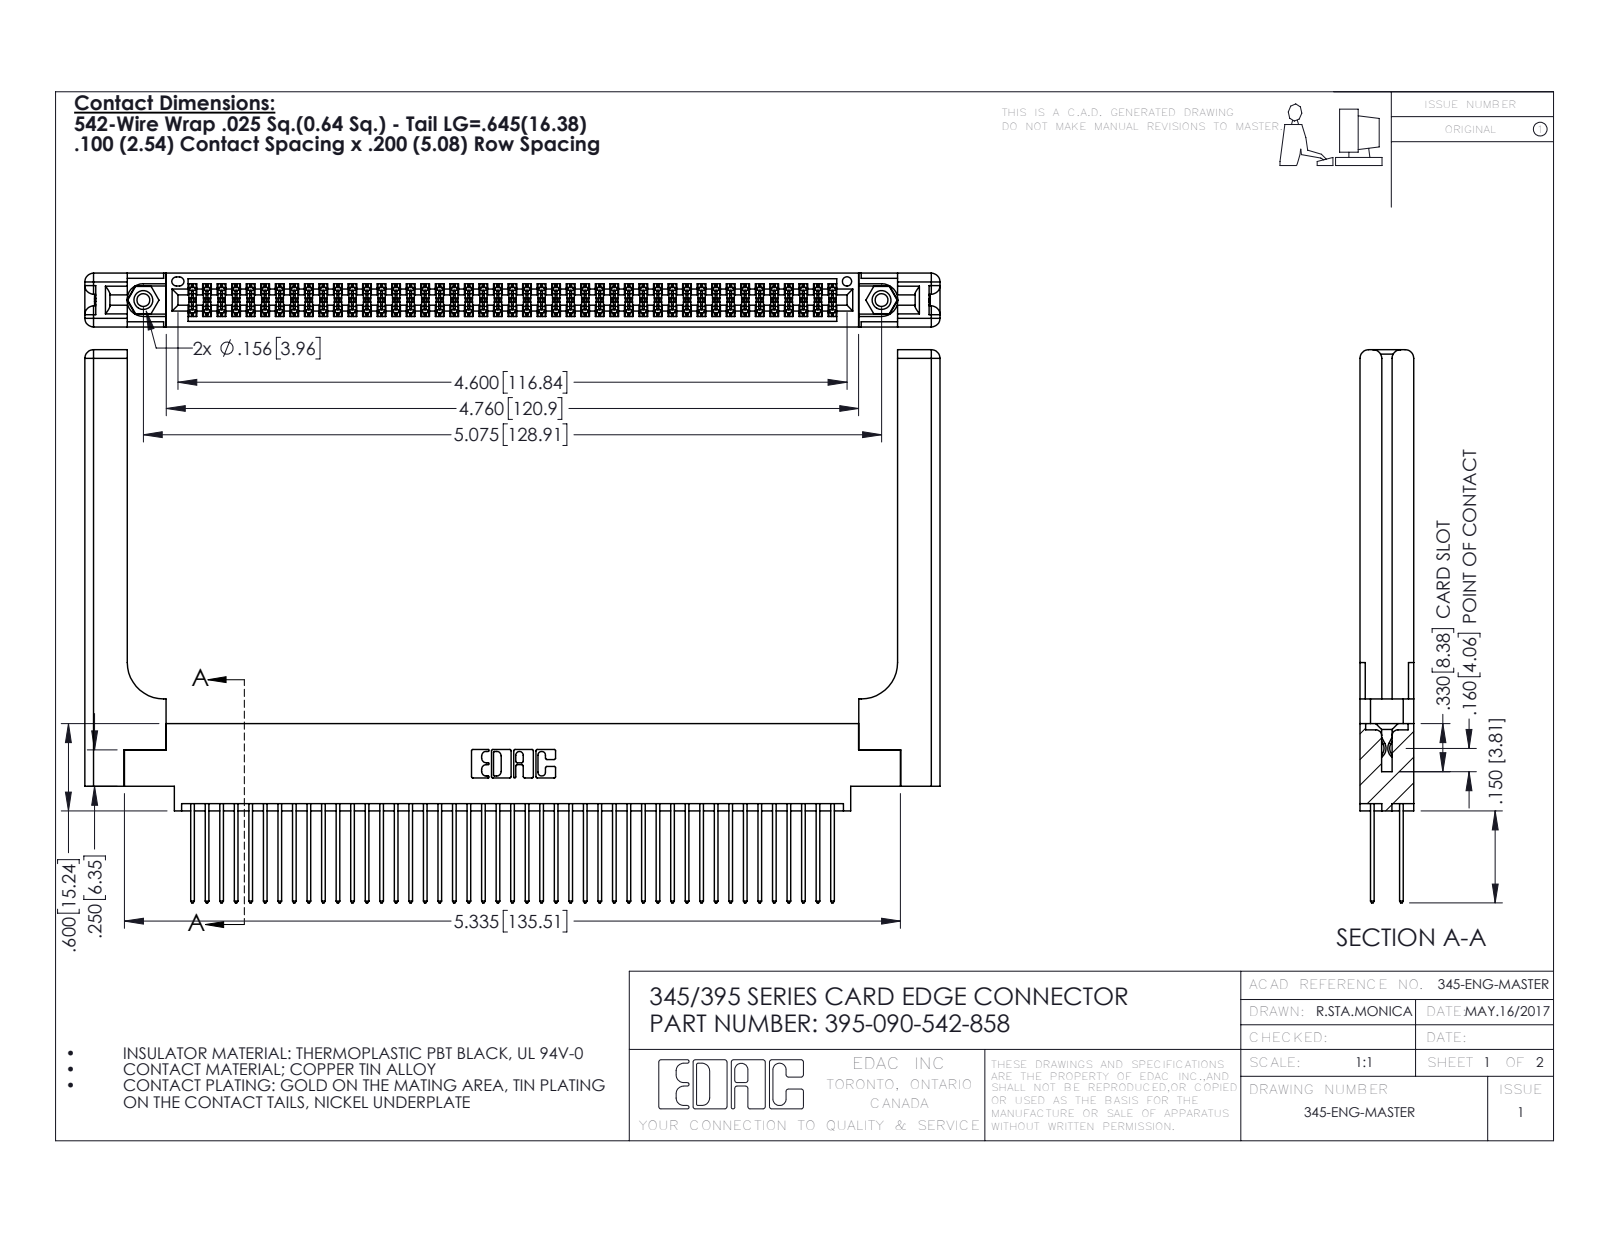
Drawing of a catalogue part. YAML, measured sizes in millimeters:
part_name: "395-090-542-858; 345 Part_0.170 Offset - 0.156 Dia-TH; 345-250-001_345-250-001-102; 345-292-001_345-293-142 (+1 more)"
step_written_by: "SolidWorks 2016 (CONFIG_CONTROL_DESIGN)"
units: millimeters
bodies: {solids: 95, faces: 4886, planar: 3202, cylindrical: 1624, other: 60}
overall_size: [149.3, 96.6, 9.4]
volume: 23320
surface_area: 29150
round_holes:
  - {diameter: 2.3, count: 2}
  - {diameter: 3.2, count: 2}
  - {diameter: 4, count: 2}
  - {diameter: 1.6, count: 1}
round_bosses_or_shafts:
  - {diameter: 3.9, count: 2}
partial_cylinders:
  - {radius: 0.2, count: 135}
  - {radius: 0.3, count: 90}
  - {radius: 0.3, count: 22}
  - {radius: 1.5, count: 16}
  - {radius: 0.2, count: 6}
  - {radius: 0.8, count: 6}
  - {radius: 0.7, count: 3}
  - {radius: 0.4, count: 2}
face_to_face_distances: [1.8, 7.6, 9.4, 2.5, 6.9, 0.6, 5.1, 5.7, 4.4, 3.8]
hole_center_spacings: [6.9, 122.9, 128.9]
